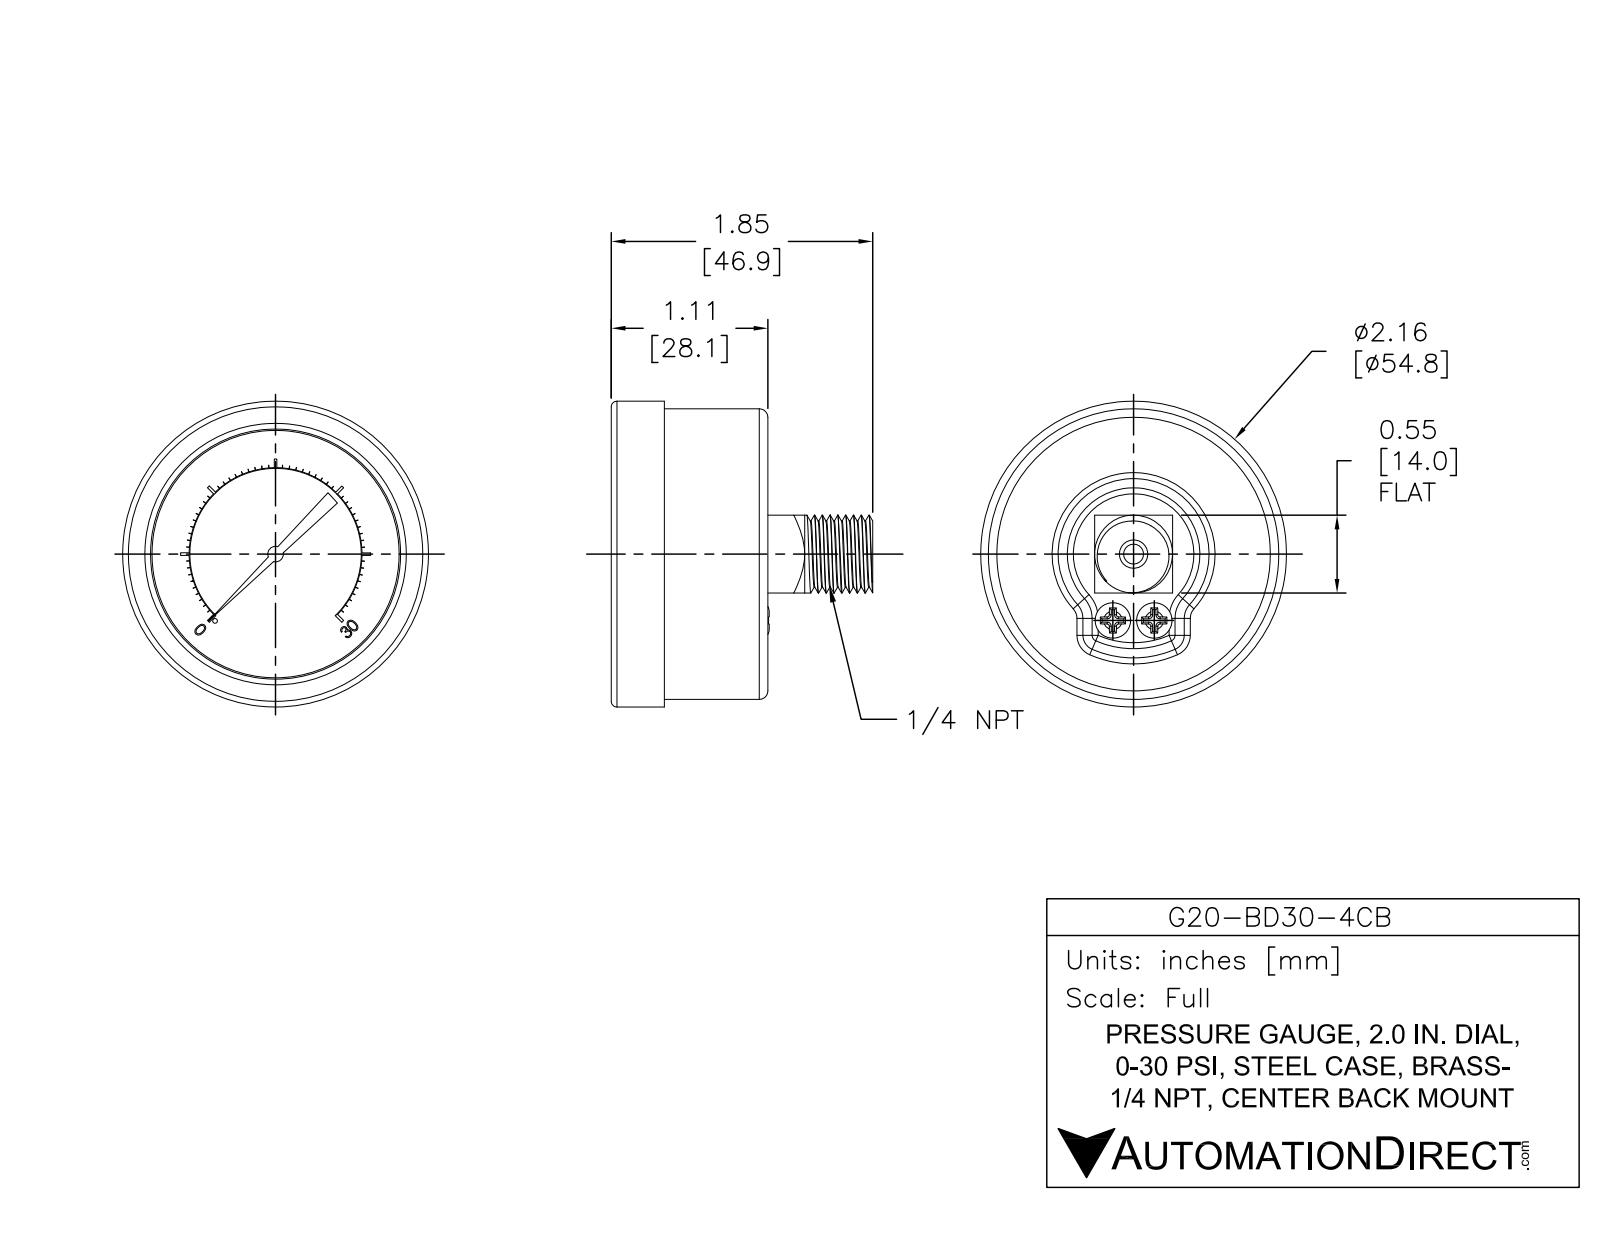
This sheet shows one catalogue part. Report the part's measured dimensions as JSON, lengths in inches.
{"part_name": "G20-BD30-4CB", "step_written_by": "SolidWorks 2021 (AUTOMOTIVE_DESIGN)", "units": "inches", "bodies": {"solids": 1, "faces": 374, "planar": 235, "cylindrical": 70, "other": 69}, "overall_size": [2.158, 2.158, 1.845], "volume_in3": 3.201, "surface_area_in2": 18.16, "round_holes": [[0.14, 1], [1.745, 1]], "round_bosses_or_shafts": [[0.25, 2], [2.158, 1], [2.05, 1], [0.55, 1], [0.11, 1], [0.102, 1], [0.055, 1]], "partial_cylinders_radius": [[0.06, 4], [0.605, 1], [0.61, 1]], "face_to_face_distances": [0.815, 1.105, 0.29, 0.73, 0.085, 0.375, 0.1, 1.005, 0.63, 0.715]}
